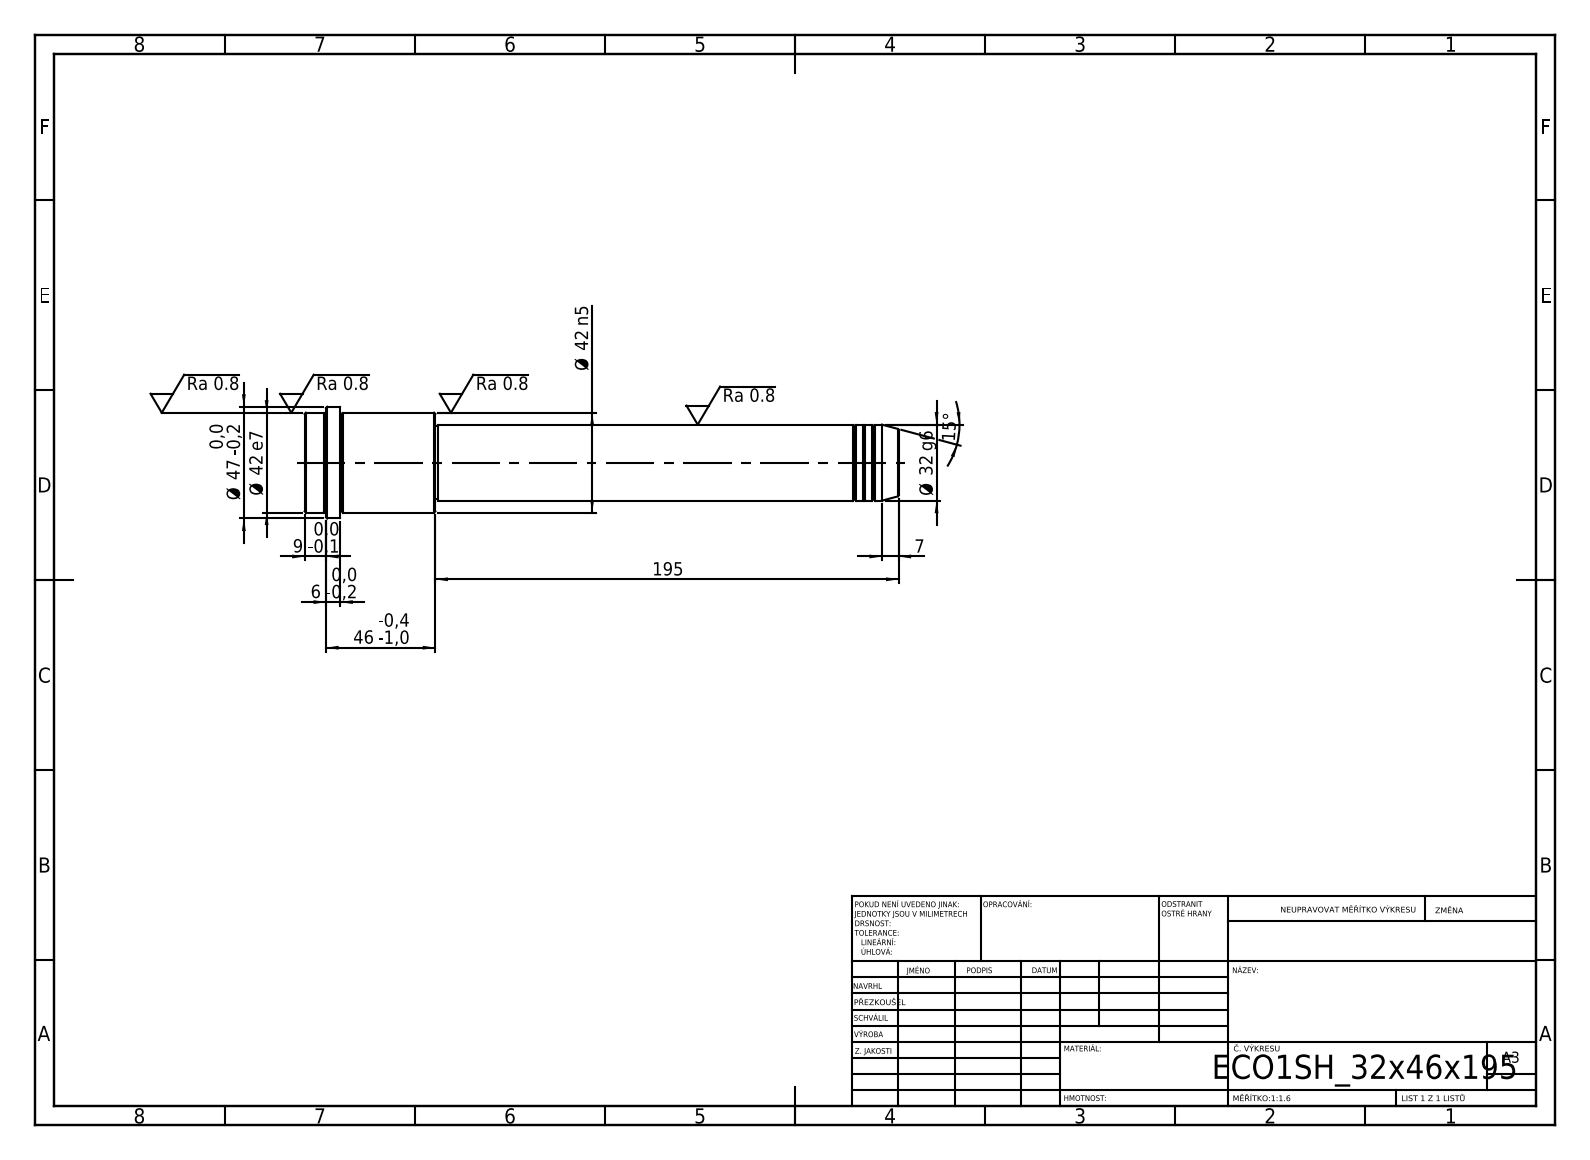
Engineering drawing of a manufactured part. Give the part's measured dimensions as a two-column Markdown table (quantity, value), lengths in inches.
| quantity | value |
| --- | --- |
| STEP written by | SolidWorks 2019 (CONFIG_CONTROL_DESIGN) |
| units | inches |
| bodies | 1 solid, 52 faces (6 planar, 16 cylindrical, 30 other) |
| overall size | 9.843 × 1.85 × 1.85 |
| volume | 14.29 in³ |
| surface area | 47.28 in² |
| round bosses / shafts (diameter × count) | 1.85 × 1, 1.654 × 1, 1.26 × 1, 1.22 × 1 |
| main face-to-face distances | 9.843, 7.677, 2.165, 9.252, 1.575, 0.591, 9.488, 1.811, 0.236, 0.354 |
